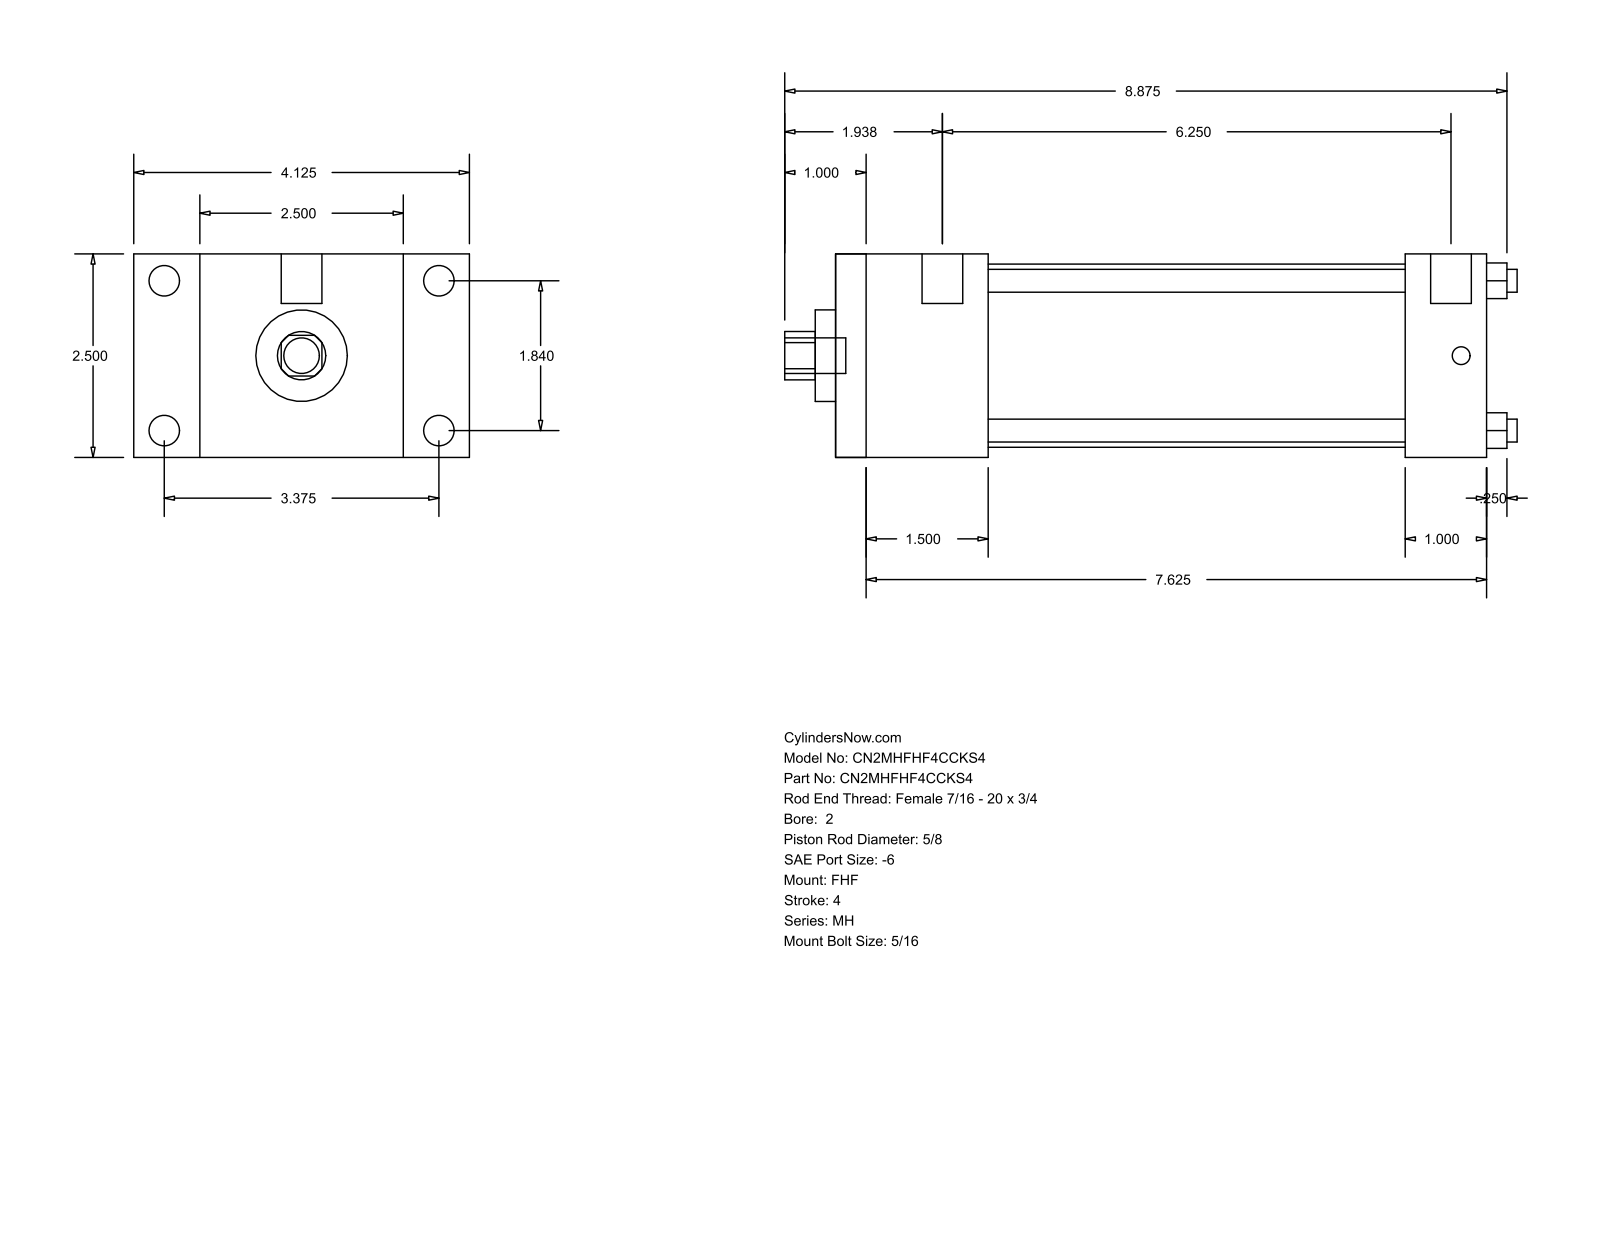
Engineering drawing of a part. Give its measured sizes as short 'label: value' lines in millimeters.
name: MH_FHF__0200_0.625
written by: GSSL Pune (CONFIG_CONTROL_DESIGN)
unit: mm
bodies: 0 solids, 88 faces (60 planar, 28 cylindrical, 0 other)
size: 228.6 × 104.78 × 63.5
holes: 4× ⌀7.14, 1× ⌀15.88, 1× ⌀28.57, 1× ⌀57.15
bosses: 4× ⌀9.53, 4× ⌀5.56, 2× ⌀12.7, 1× ⌀11.11
rounds: 1× R7.54
face distances: 63.5, 47.62, 203.19, 155.57, 20.64, 84.14, 104.78, 177.8, 130.18, 25.39
hole spacings: 33.05, 46.74, 66.1
